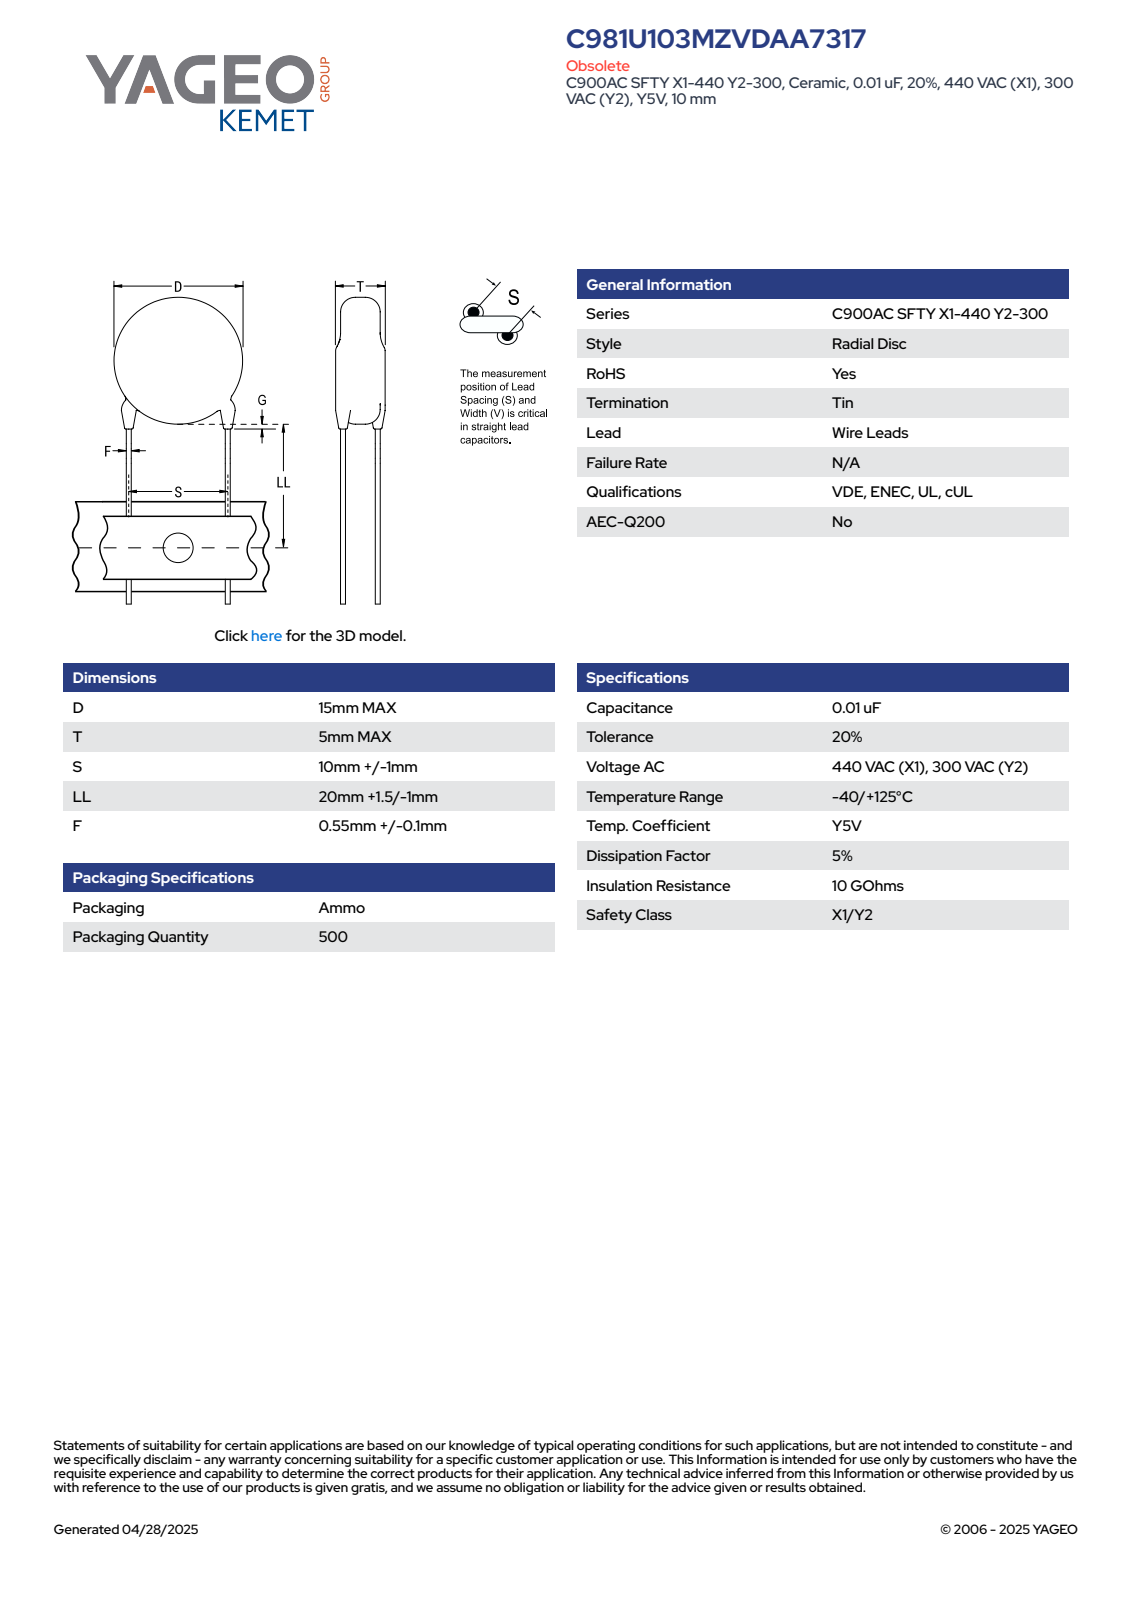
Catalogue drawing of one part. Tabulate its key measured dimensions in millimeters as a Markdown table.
| quantity | value |
| --- | --- |
| part name | CCD_STC900_D15T5S10LL21.5F0.65G3 |
| STEP written by | SolidWorks 2014 (AUTOMOTIVE_DESIGN) |
| units | millimeters |
| bodies | 4 solids, 83 faces (61 planar, 6 cylindrical, 16 other) |
| overall size | 36.5 × 15 × 5 |
| volume | 881 mm³ |
| surface area | 661 mm² |
| round bosses / shafts (diameter × count) | 0.65 × 2, 15 × 1 |
| main face-to-face distances | 5, 29.86, 28.13, 1.73, 0.33, 1.4, 0.32, 5.13, 5.33, 28.46 |
